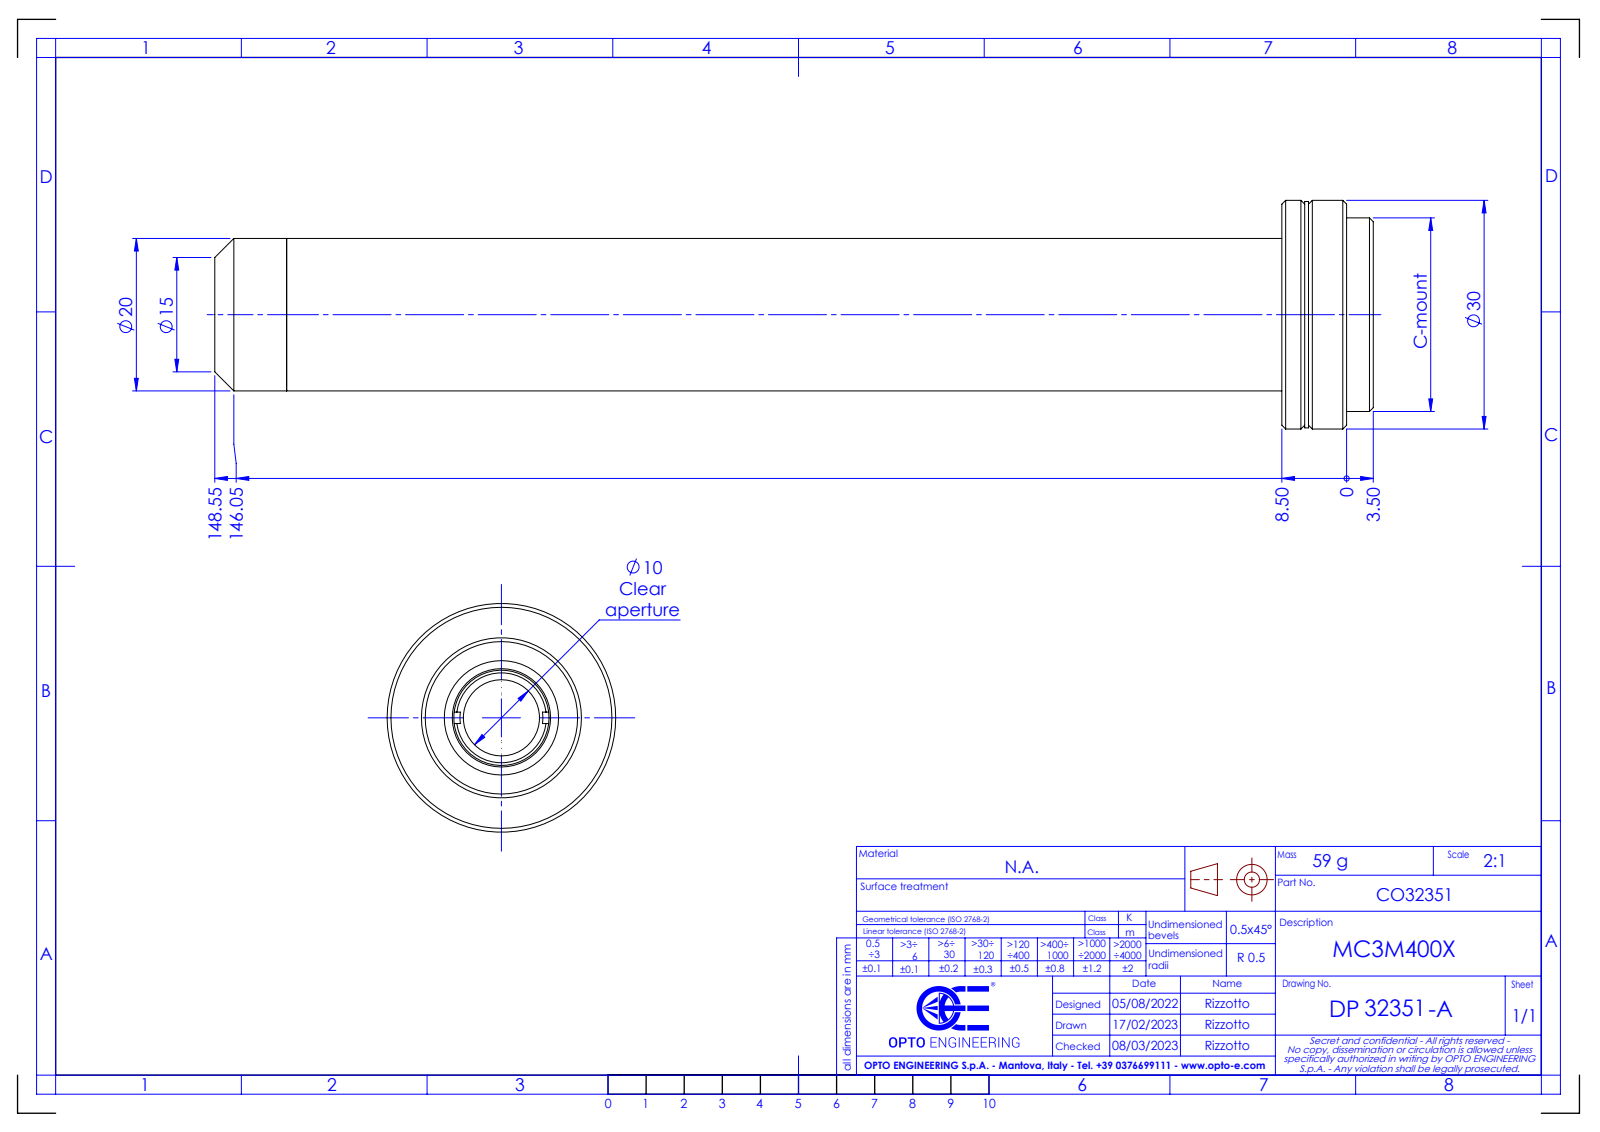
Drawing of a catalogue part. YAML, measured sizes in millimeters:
part_name: "DP32351-A_MC3M400X"
step_written_by: "SolidWorks 2021 (CONFIG_CONTROL_DESIGN)"
units: millimeters
bodies: {solids: 0, faces: 64, planar: 16, cylindrical: 22, other: 26}
overall_size: [152.05, 30, 30]
round_holes:
  - {diameter: 10, count: 1}
  - {diameter: 12.5, count: 1}
  - {diameter: 17.5, count: 1}
  - {diameter: 18, count: 1}
round_bosses_or_shafts:
  - {diameter: 30, count: 1}
  - {diameter: 29.7, count: 1}
  - {diameter: 25.4, count: 1}
  - {diameter: 20, count: 1}
face_to_face_distances: [8.5, 3.5, 5, 3, 0.5, 5.5, 12, 9, 130.62, 133.62]
